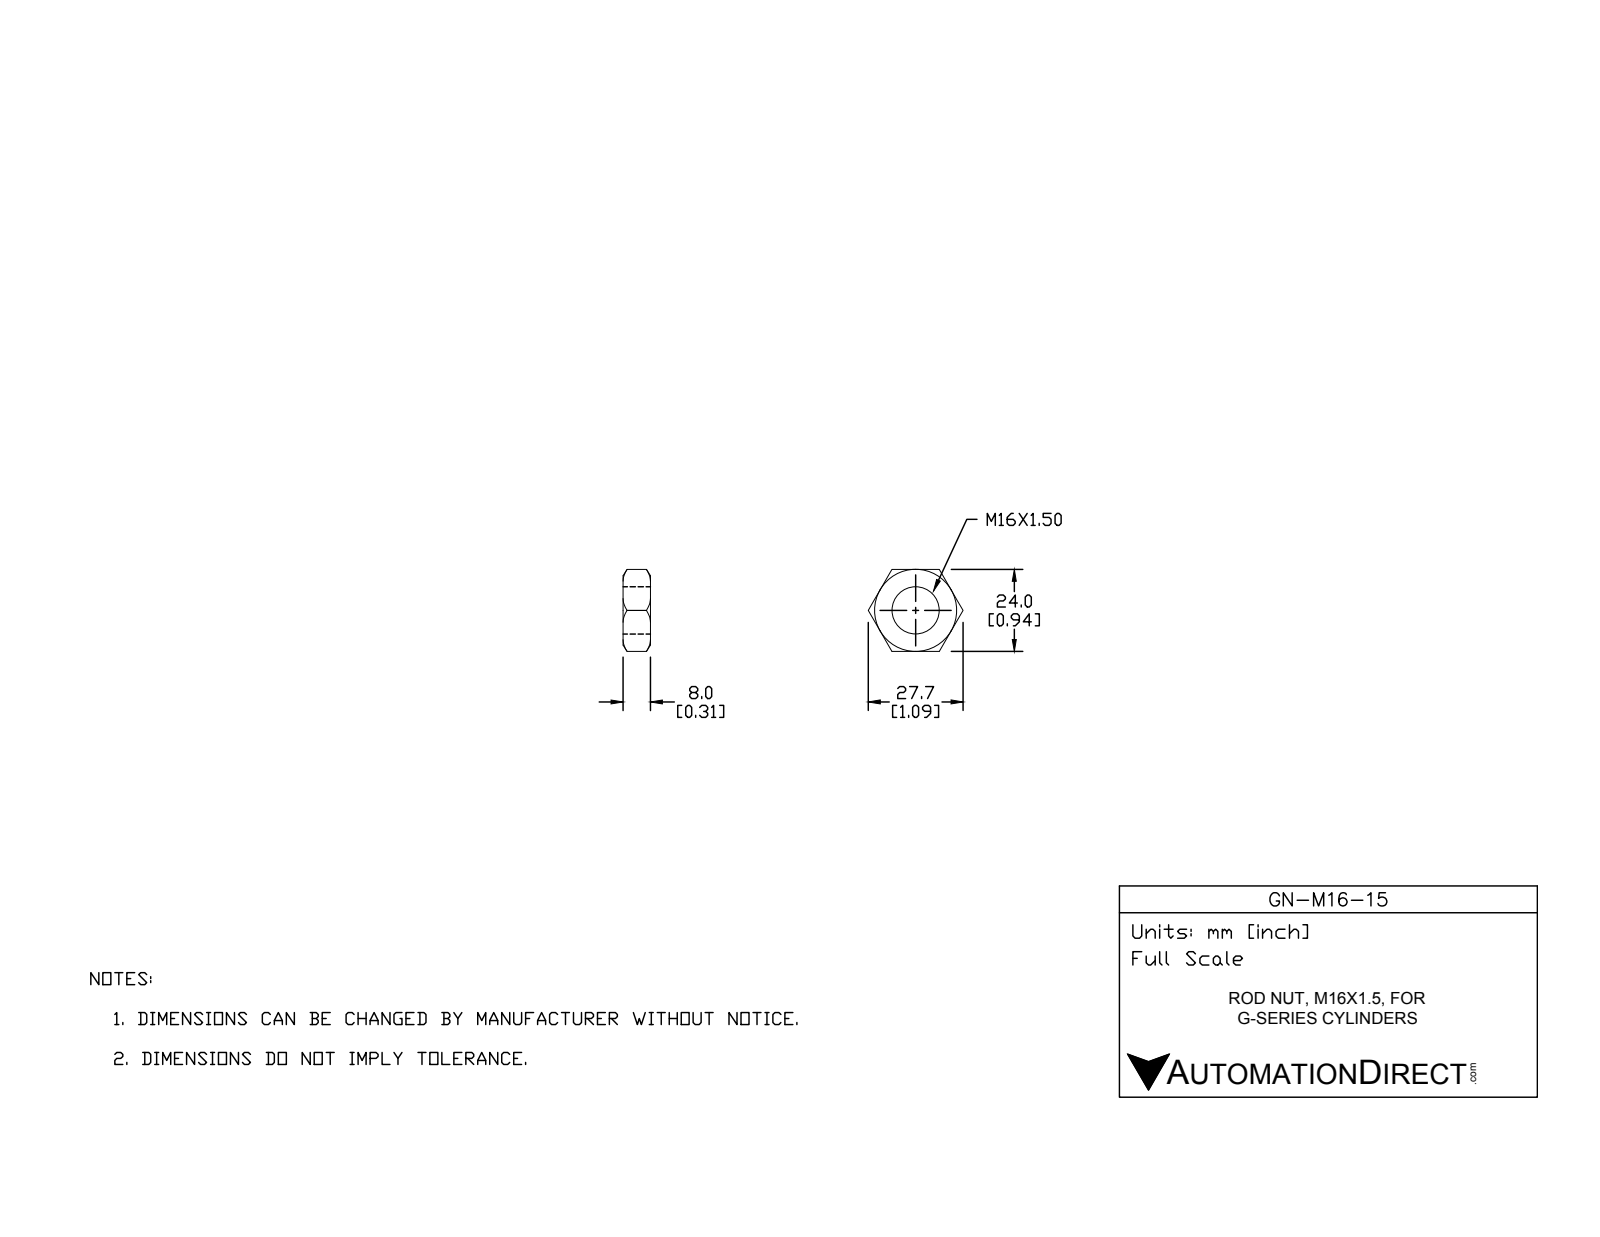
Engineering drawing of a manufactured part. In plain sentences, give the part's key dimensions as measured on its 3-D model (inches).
The part is named "GN-M16-15". Its 3-D file was written by "SolidWorks 2017 (AUTOMOTIVE_DESIGN)". It is 1 solid with 24 faces: 8 planar, 2 cylindrical and 14 other. Overall it measures 1.091 by 0.945 by 0.315 inches. Its volume is 0.16 cubic inches and its surface area 2.527 square inches. Round holes: 1 of diameter 0.571. The main face-to-face distances are 0.315, 0.945.
